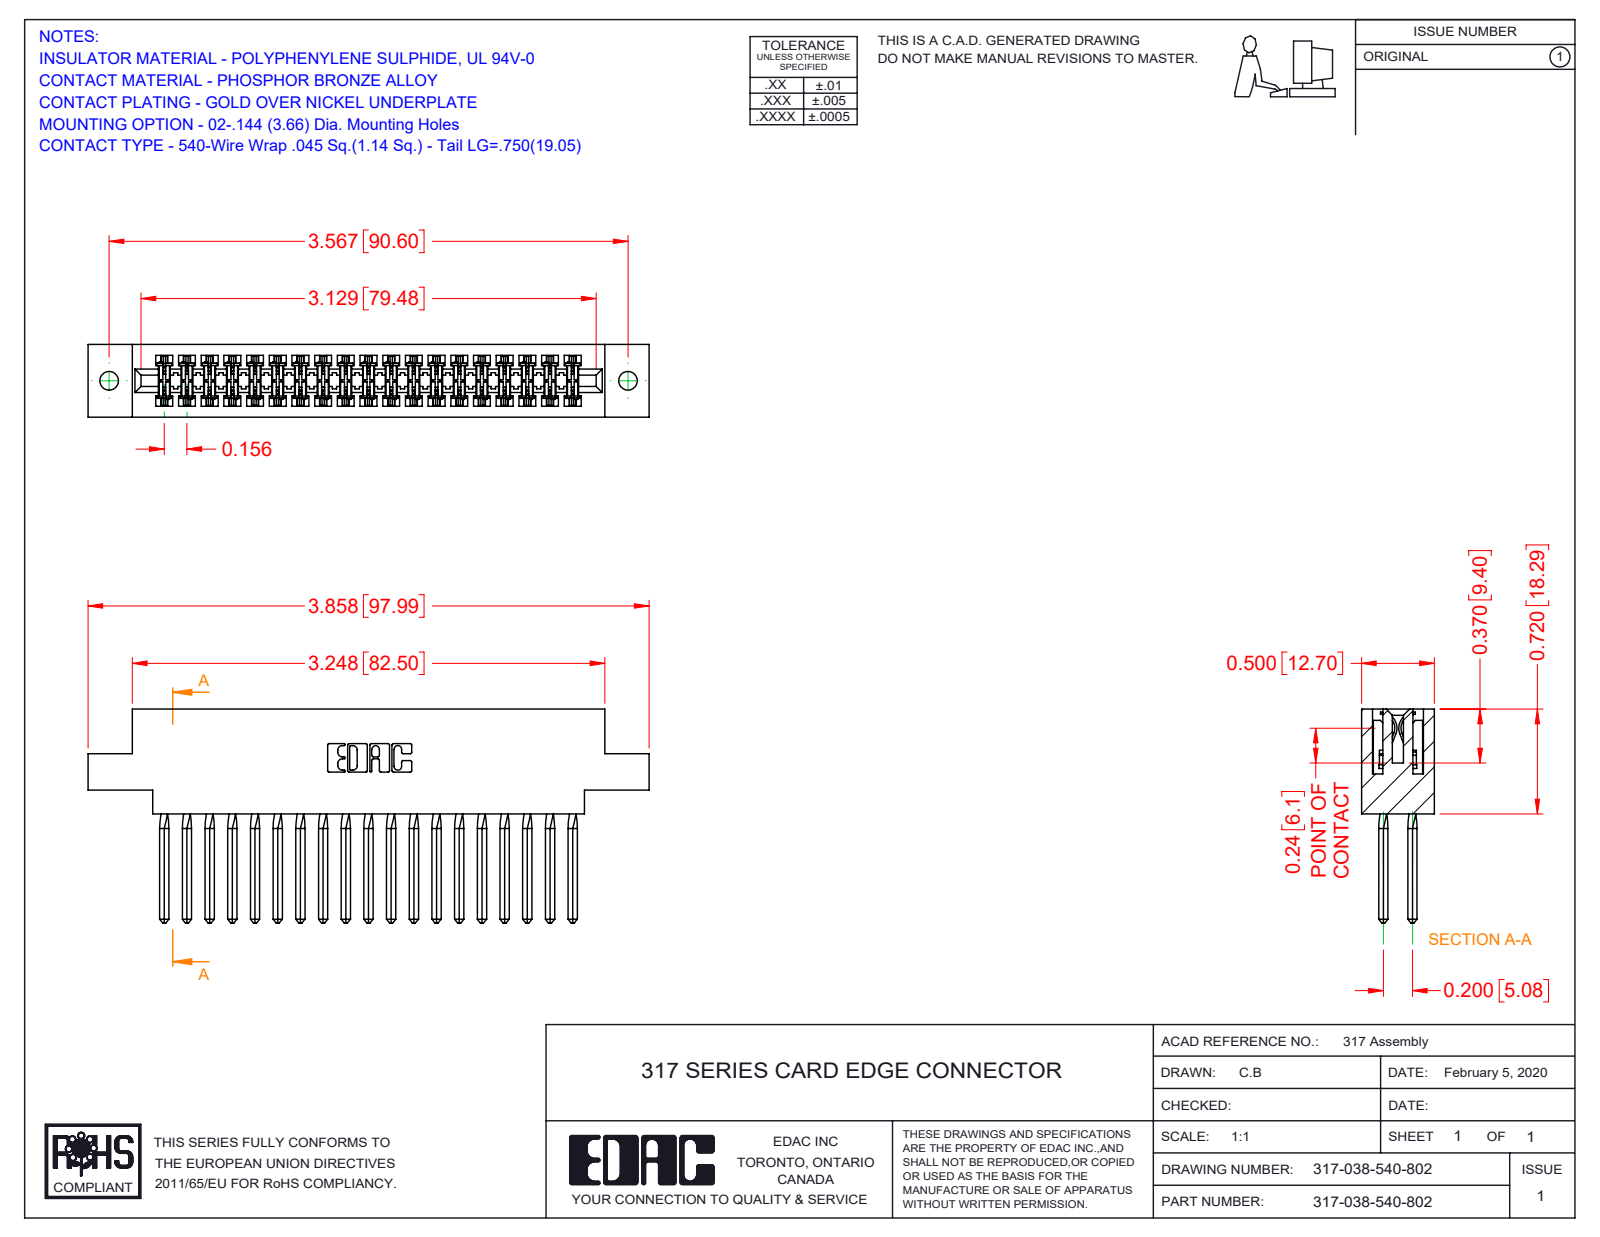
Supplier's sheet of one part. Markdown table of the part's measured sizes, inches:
| quantity | value |
| --- | --- |
| part name | 317-290-001_540; 317-038-540-802; 317 Part_.144 Dia |
| STEP written by | SolidWorks 2016 (CONFIG_CONTROL_DESIGN) |
| units | inches |
| bodies | 39 solids, 3484 faces (2832 planar, 500 cylindrical, 152 other) |
| overall size | 3.858 × 1.47 × 0.5 |
| volume | 0.954 in³ |
| surface area | 34.37 in² |
| round holes (diameter × count) | 0.128 × 2 |
| partial cylindrical surfaces (radius × count) | 0.015 × 76, 0.01 × 22, 0.007 × 6, 0.031 × 6, 0.026 × 3, 0.095 × 2, 0.1 × 2, 0.11 × 2 |
| main face-to-face distances | 0.5, 0.075, 0.425, 0.11, 0.35, 0.195, 0.22, 0.72, 0.094, 0.2 |
| hole center spacings | 3.567 |
